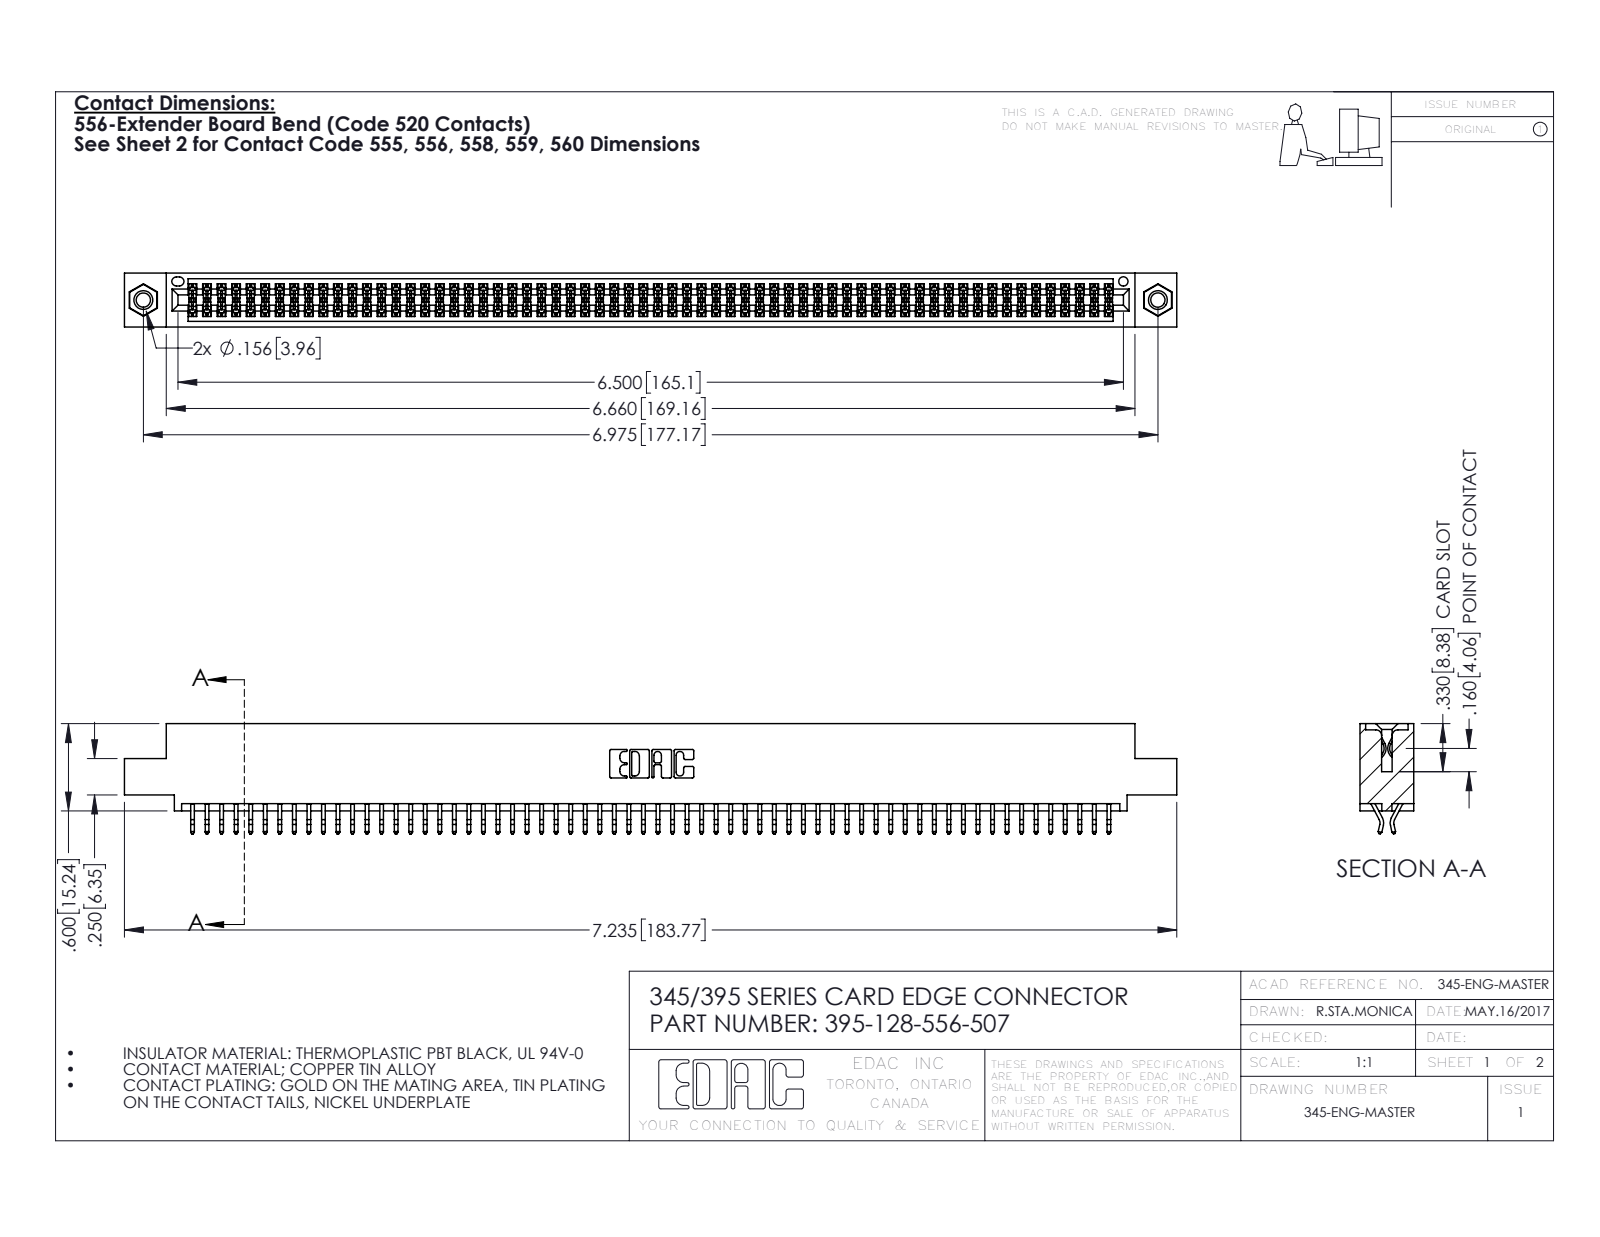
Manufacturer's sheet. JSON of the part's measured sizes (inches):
{"part_name": "395-128-556-507; 345-292-001_556 Tail; 345-250-001_345-250-005-103; 345 Part_0.110 Offset - 0.156 Dia-TI", "step_written_by": "SolidWorks 2016 (CONFIG_CONTROL_DESIGN)", "units": "inches", "bodies": {"solids": 131, "faces": 7358, "planar": 4852, "cylindrical": 2490, "other": 16}, "overall_size": [7.235, 0.757, 0.37], "volume_in3": 1.096, "surface_area_in2": 41.83, "round_holes": [[0.098, 2], [0.125, 2], [0.156, 2], [0.064, 1]], "round_bosses_or_shafts": [[0.155, 2]], "partial_cylinders_radius": [[0.006, 192], [0.01, 22], [0.007, 6], [0.031, 6], [0.026, 3], [0.01, 2], [0.014, 2], [0.019, 2]], "face_to_face_distances": [0.072, 0.298, 0.37, 0.2, 0.025, 0.098, 0.272, 0.225, 0.175, 0.149], "hole_center_spacings": [0.27, 6.739, 6.975]}
